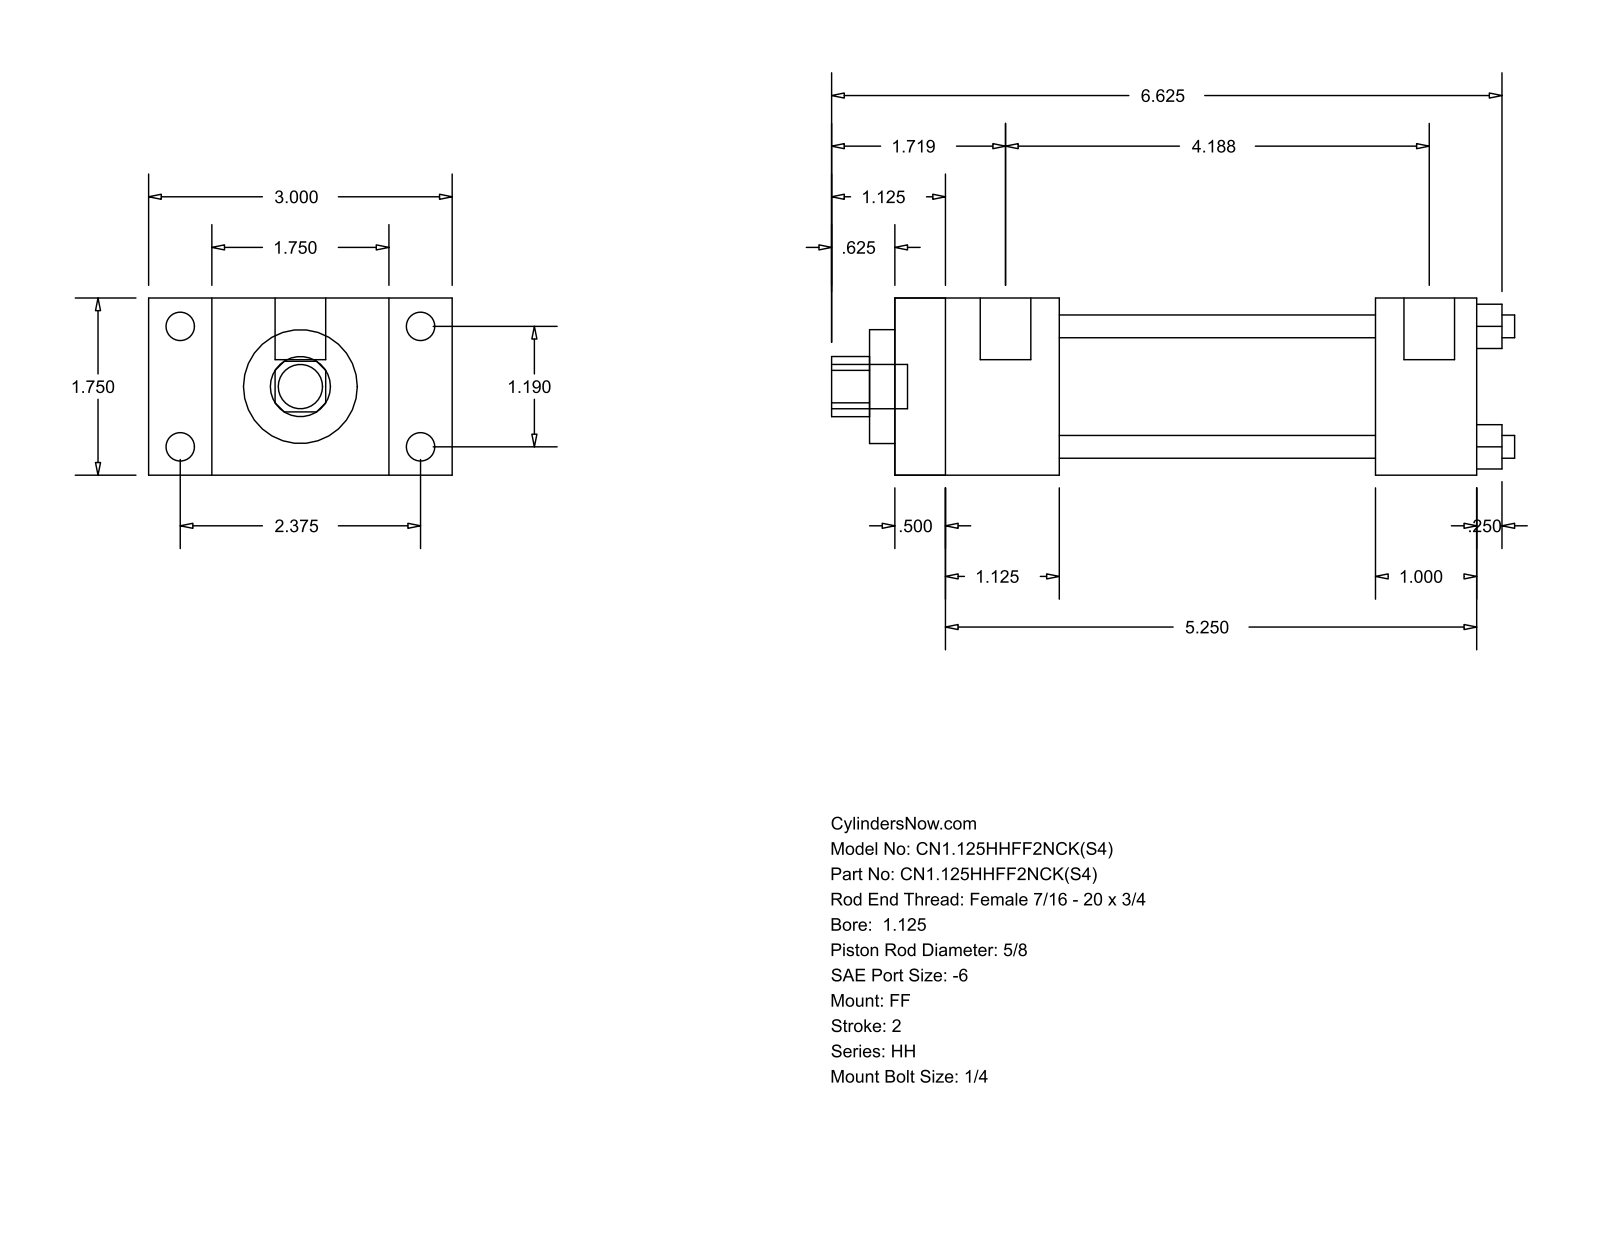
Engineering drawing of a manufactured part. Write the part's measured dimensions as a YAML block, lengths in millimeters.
part_name: "HH_FF__0112_0.625"
step_written_by: "GSSL Pune (CONFIG_CONTROL_DESIGN)"
units: millimeters
bodies: {solids: 0, faces: 92, planar: 64, cylindrical: 28, other: 0}
overall_size: [171.45, 76.2, 44.45]
round_holes:
  - {diameter: 5.71, count: 4}
  - {diameter: 15.88, count: 1}
  - {diameter: 28.57, count: 1}
  - {diameter: 34.92, count: 1}
round_bosses_or_shafts:
  - {diameter: 7.14, count: 4}
  - {diameter: 5.56, count: 4}
  - {diameter: 12.7, count: 2}
  - {diameter: 11.11, count: 1}
partial_cylinders:
  - {radius: 7.54, count: 1}
face_to_face_distances: [44.46, 146.05, 15.87, 12.69, 133.36, 60.33, 28.58, 41.27, 120.65, 107.96]
hole_center_spacings: [21.37, 30.22, 42.74]
